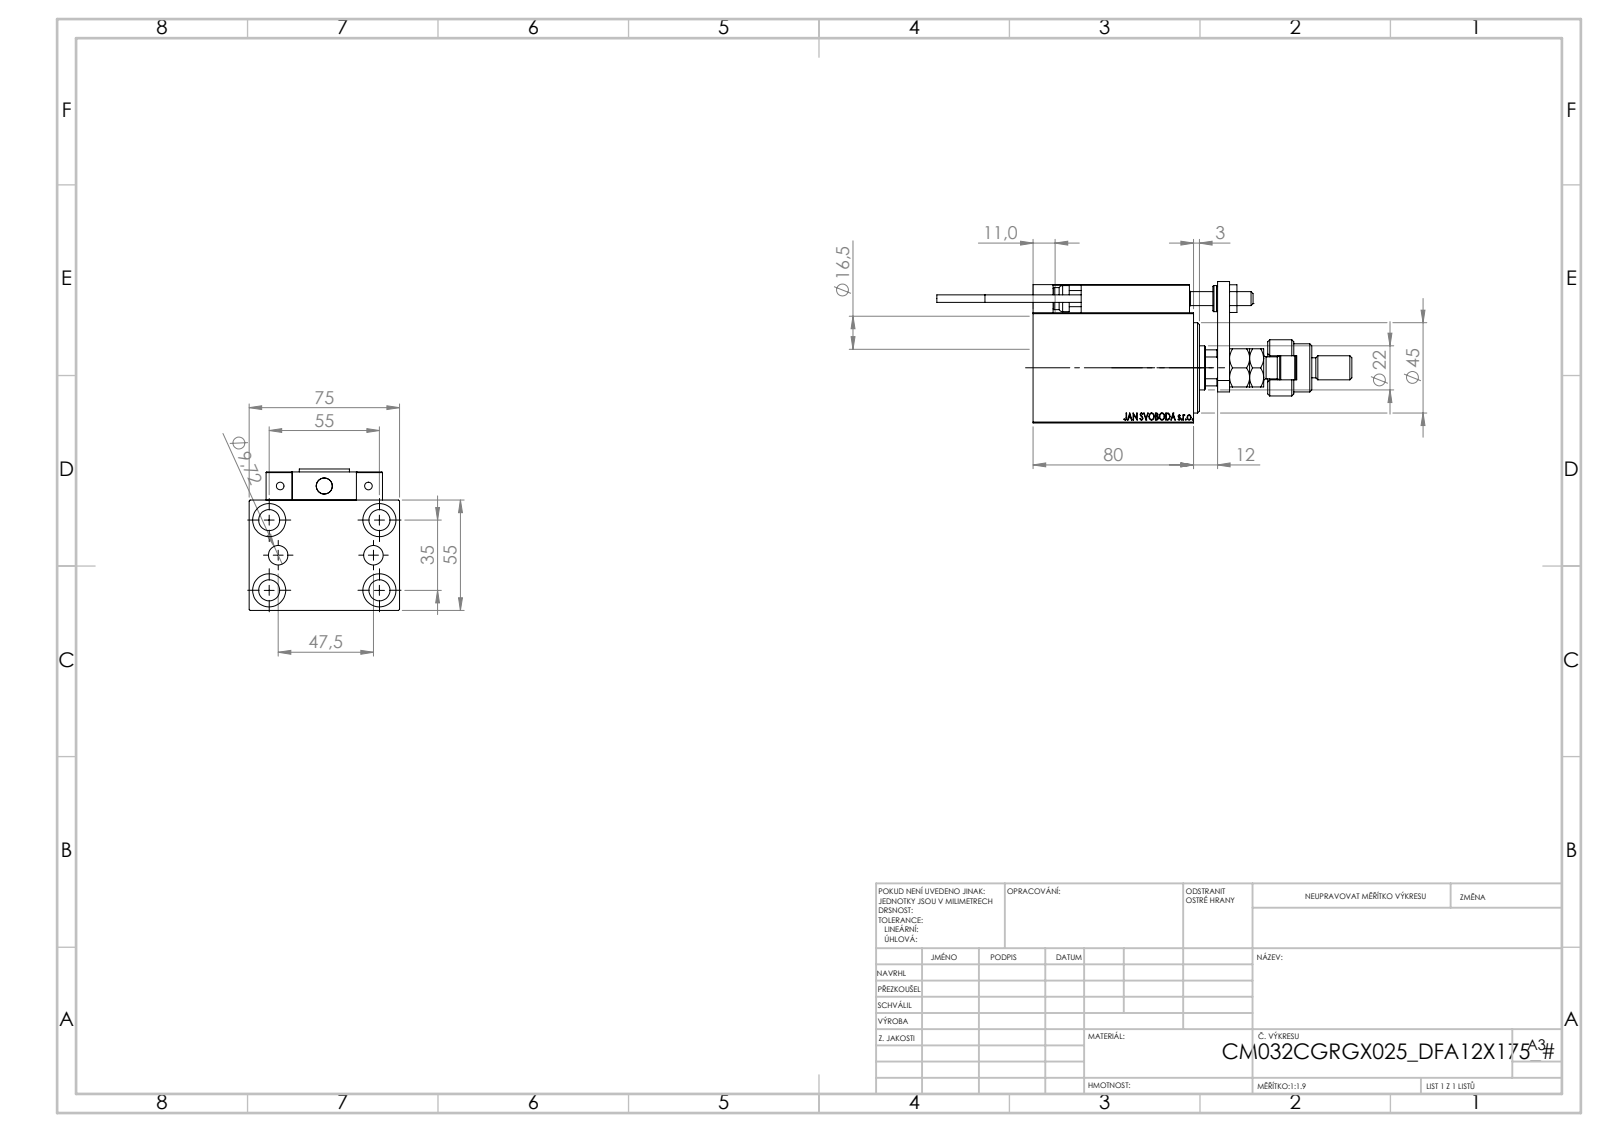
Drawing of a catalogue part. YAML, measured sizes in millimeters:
part_name: "ALLEN BOLT D8; MFA; X_Y_DFA; KONCOVKA (+7 more)"
step_written_by: "SolidWorks 2019 (CONFIG_CONTROL_DESIGN)"
units: millimeters
bodies: {solids: 25, faces: 1363, planar: 588, cylindrical: 197, other: 578}
overall_size: [207, 75, 70.5]
volume: 348779
surface_area: 91722
round_holes:
  - {diameter: 4, count: 6}
  - {diameter: 8, count: 5}
  - {diameter: 10.5, count: 5}
  - {diameter: 16.5, count: 5}
  - {diameter: 3.2, count: 4}
  - {diameter: 5, count: 2}
  - {diameter: 9.72, count: 2}
  - {diameter: 7, count: 1}
  - {diameter: 22, count: 1}
  - {diameter: 25.5, count: 1}
  - {diameter: 32, count: 1}
  - {diameter: 34, count: 1}
round_bosses_or_shafts:
  - {diameter: 11, count: 2}
  - {diameter: 5, count: 2}
  - {diameter: 3.8, count: 2}
  - {diameter: 28, count: 1}
  - {diameter: 24, count: 1}
  - {diameter: 18, count: 1}
  - {diameter: 13, count: 1}
  - {diameter: 12, count: 1}
partial_cylinders:
  - {radius: 0.3, count: 30}
  - {radius: 3, count: 2}
  - {radius: 9.75, count: 1}
  - {radius: 10.5, count: 1}
face_to_face_distances: [55, 75, 14, 69, 25, 5, 18, 23, 6, 12]
hole_center_spacings: [17.9, 32.6, 54.16, 11.37, 20, 23.75, 29.59, 29.69]
